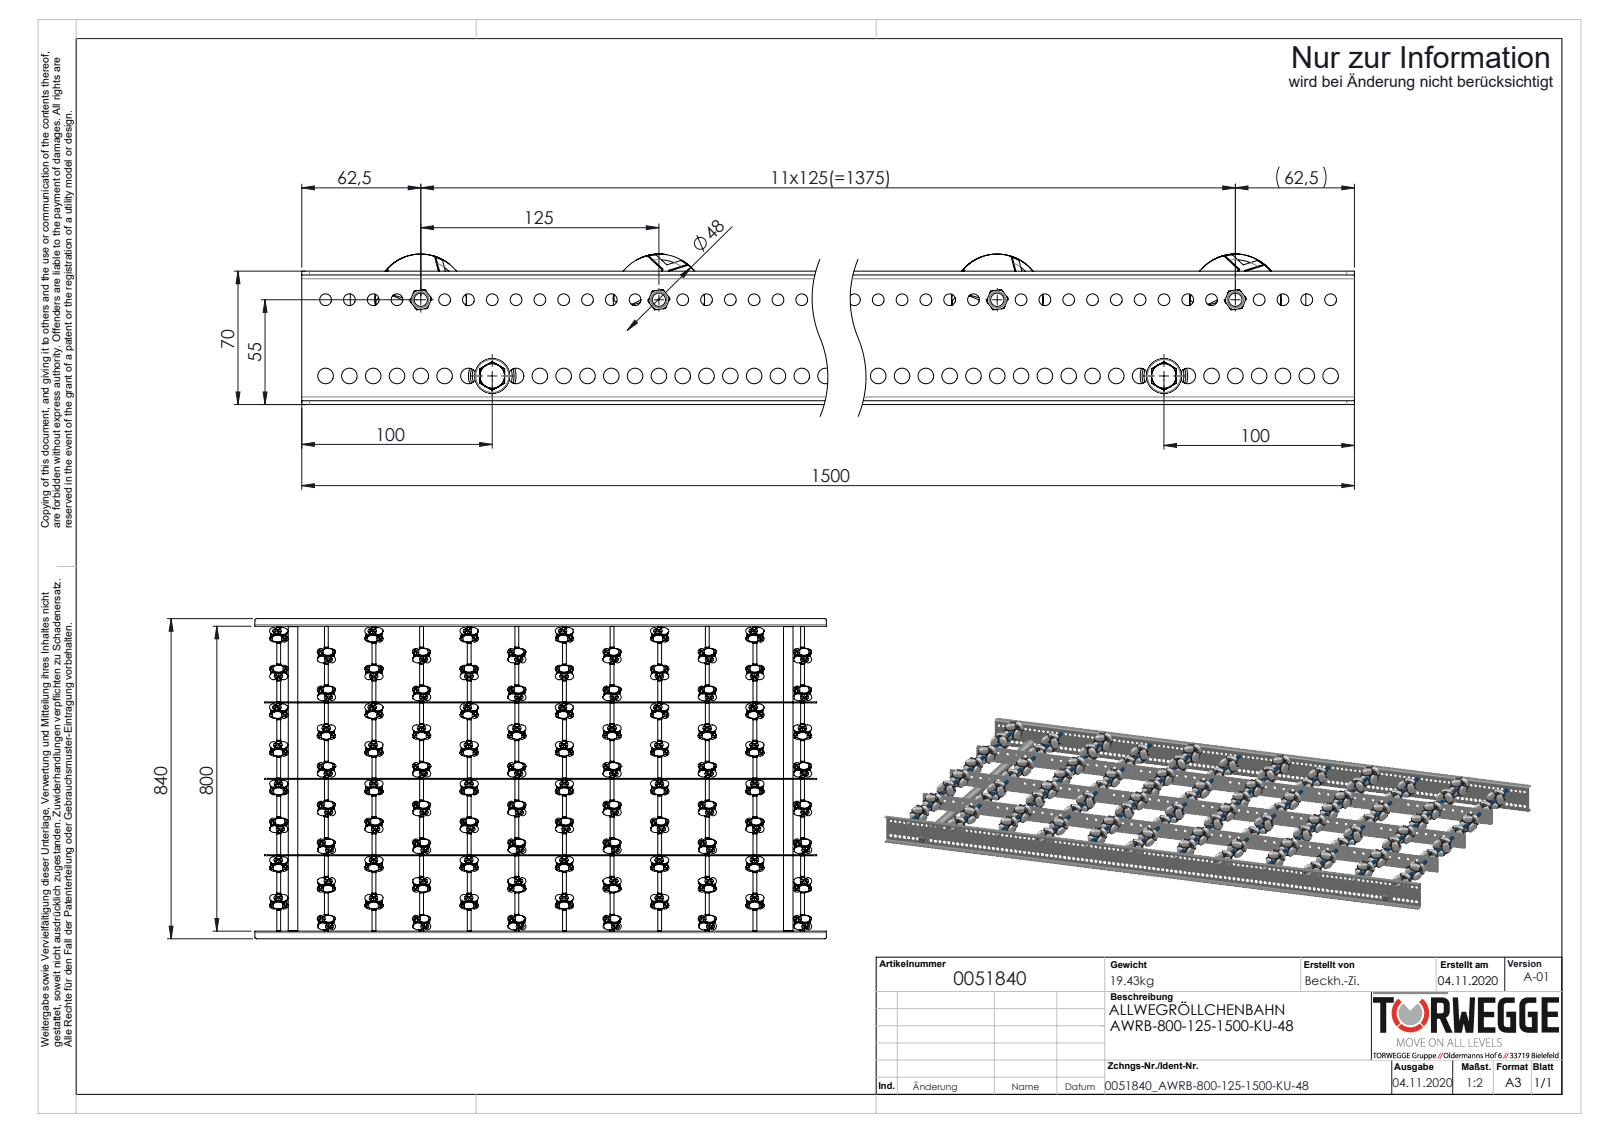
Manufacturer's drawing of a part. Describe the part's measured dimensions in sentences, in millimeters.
The part is named "0036819_SICHERUNGS-HUTMUTTER-DIN986-M6; S108767_Längstraverse-42x2,5-AWR_L1449; AWR48_Röllchen; AWR48_Halter (+8 more)". Its 3-D file was written by "SolidWorks 2020 (AUTOMOTIVE_DESIGN)". It is 1587 solids with 28514 faces: 9762 planar, 11472 cylindrical and 7280 other. Overall it measures 1500 by 840 by 79 millimeters. Its volume is 5 878 000 cubic millimeters and its surface area 4 136 000 square millimeters. Round holes: 576 of diameter 3.7, 576 of diameter 4.2, 119 of diameter 6.2, 119 of diameter 8.2, 58 of diameter 6.5, 12 of diameter 4.92, 12 of diameter 8.4, 2 of diameter 6.8, 2 of diameter 21. Round bosses or shafts: 576 of diameter 4, 502 of diameter 3.7, 14 of diameter 8, 12 of diameter 47.1, 12 of diameter 42, 12 of diameter 11, 12 of diameter 10, 12 of diameter 7. Partial cylindrical surfaces (rounded edges, fillets, slot ends): 8 of radius 4, 4 of radius 2, 4 of radius 5. The main face-to-face distances are 2, 200.5, 2.5, 802, 401, 203, 198, 68, 800, 804. The hole center spacings are 36.05, 36.06, 99, 36.07, 122.72, 36.04, 7.75, 10.
